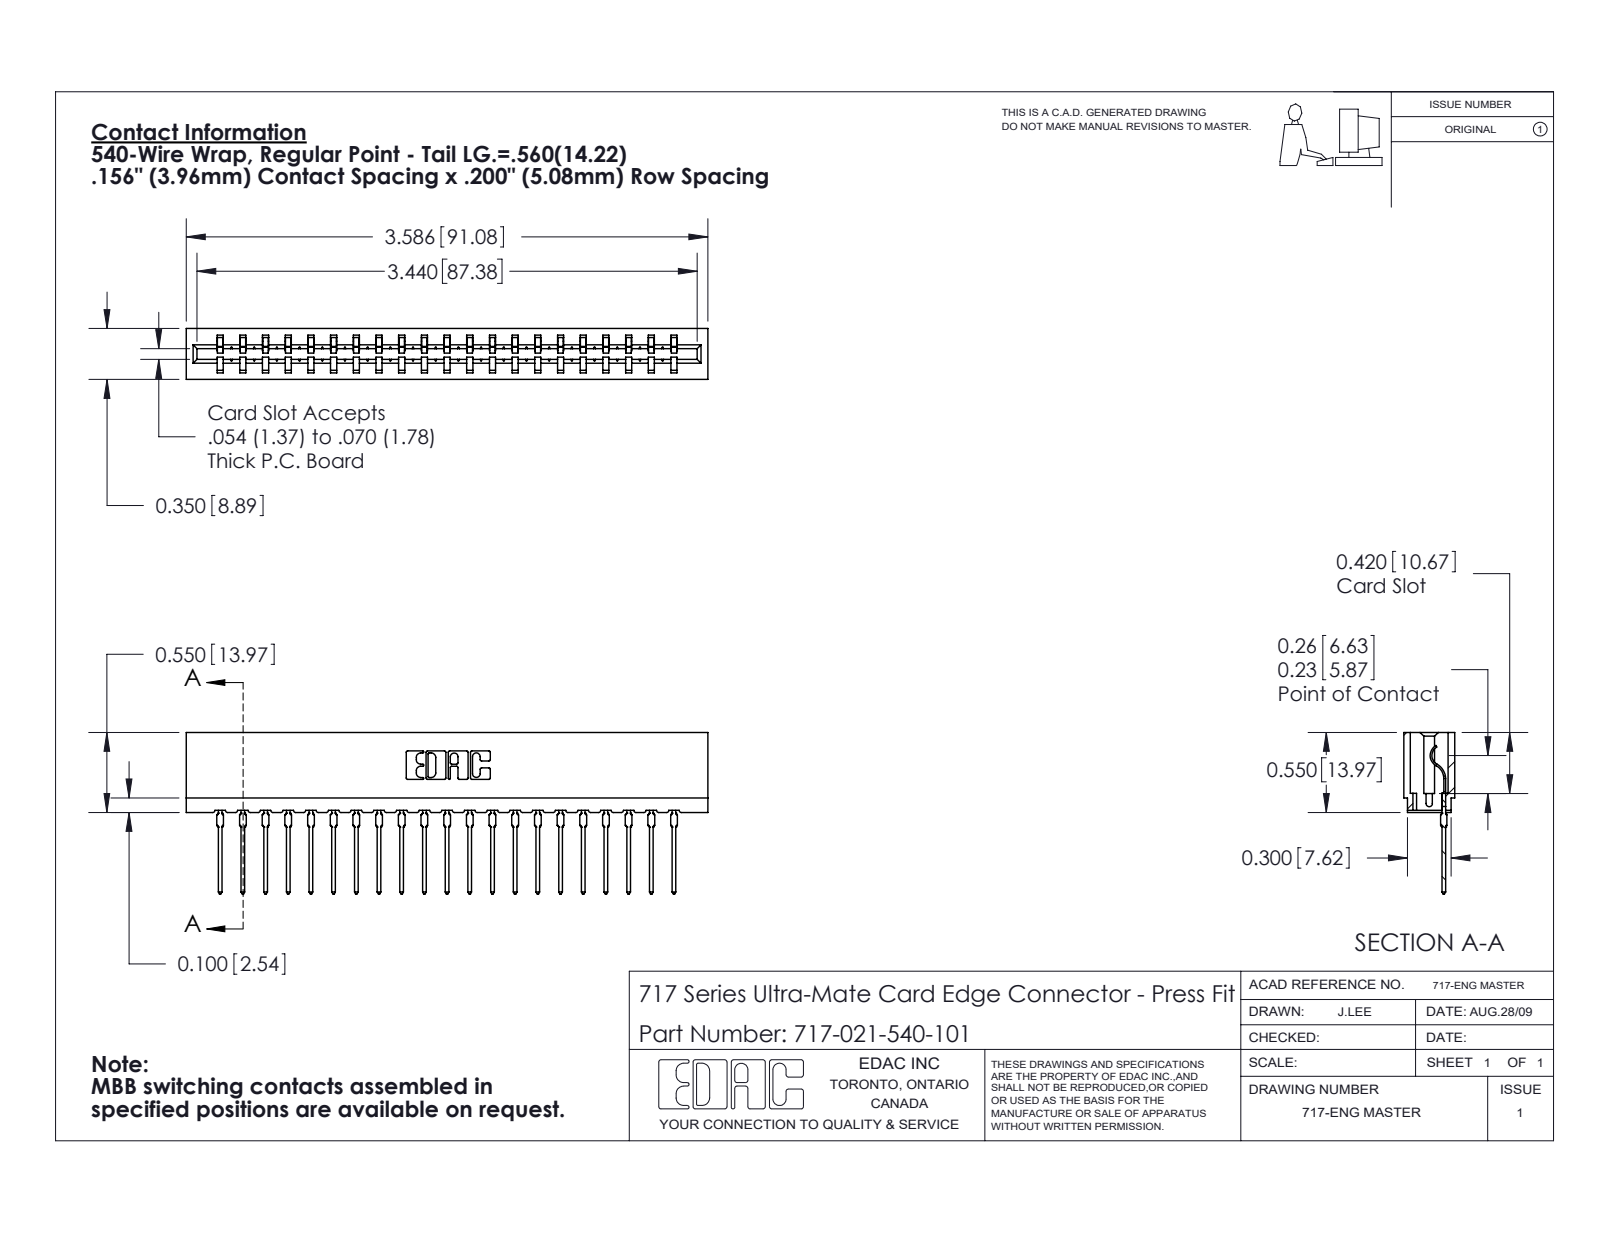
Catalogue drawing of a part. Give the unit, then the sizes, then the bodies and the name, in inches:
Units: inches
Overall size (bounding box): 3.586 × 1.109 × 0.35
Partial cylindrical surfaces — rounded edges, fillets, slot ends (radius × count): R0.015 ×42, R0.021 ×42, R0.01 ×22, R0.007 ×6, R0.031 ×6, R0.005 ×4, R0.011 ×4, R0.026 ×3
Main face-to-face distances: 0.212, 0.138, 0.35, 0.156, 0.624, 0.074, 0.468, 0.063, 0.287, 0.076
Volume: 0.478 in³ · Surface area: 17.08 in²
Bodies: 22 solids, 2467 faces (1482 planar, 439 cylindrical, 546 other)
Part name (STEP PRODUCT): 717 Part_Insulator Option - 06; 717-021-540-101; 745-292-001_540
STEP written by: SolidWorks 2020 (CONFIG_CONTROL_DESIGN)
